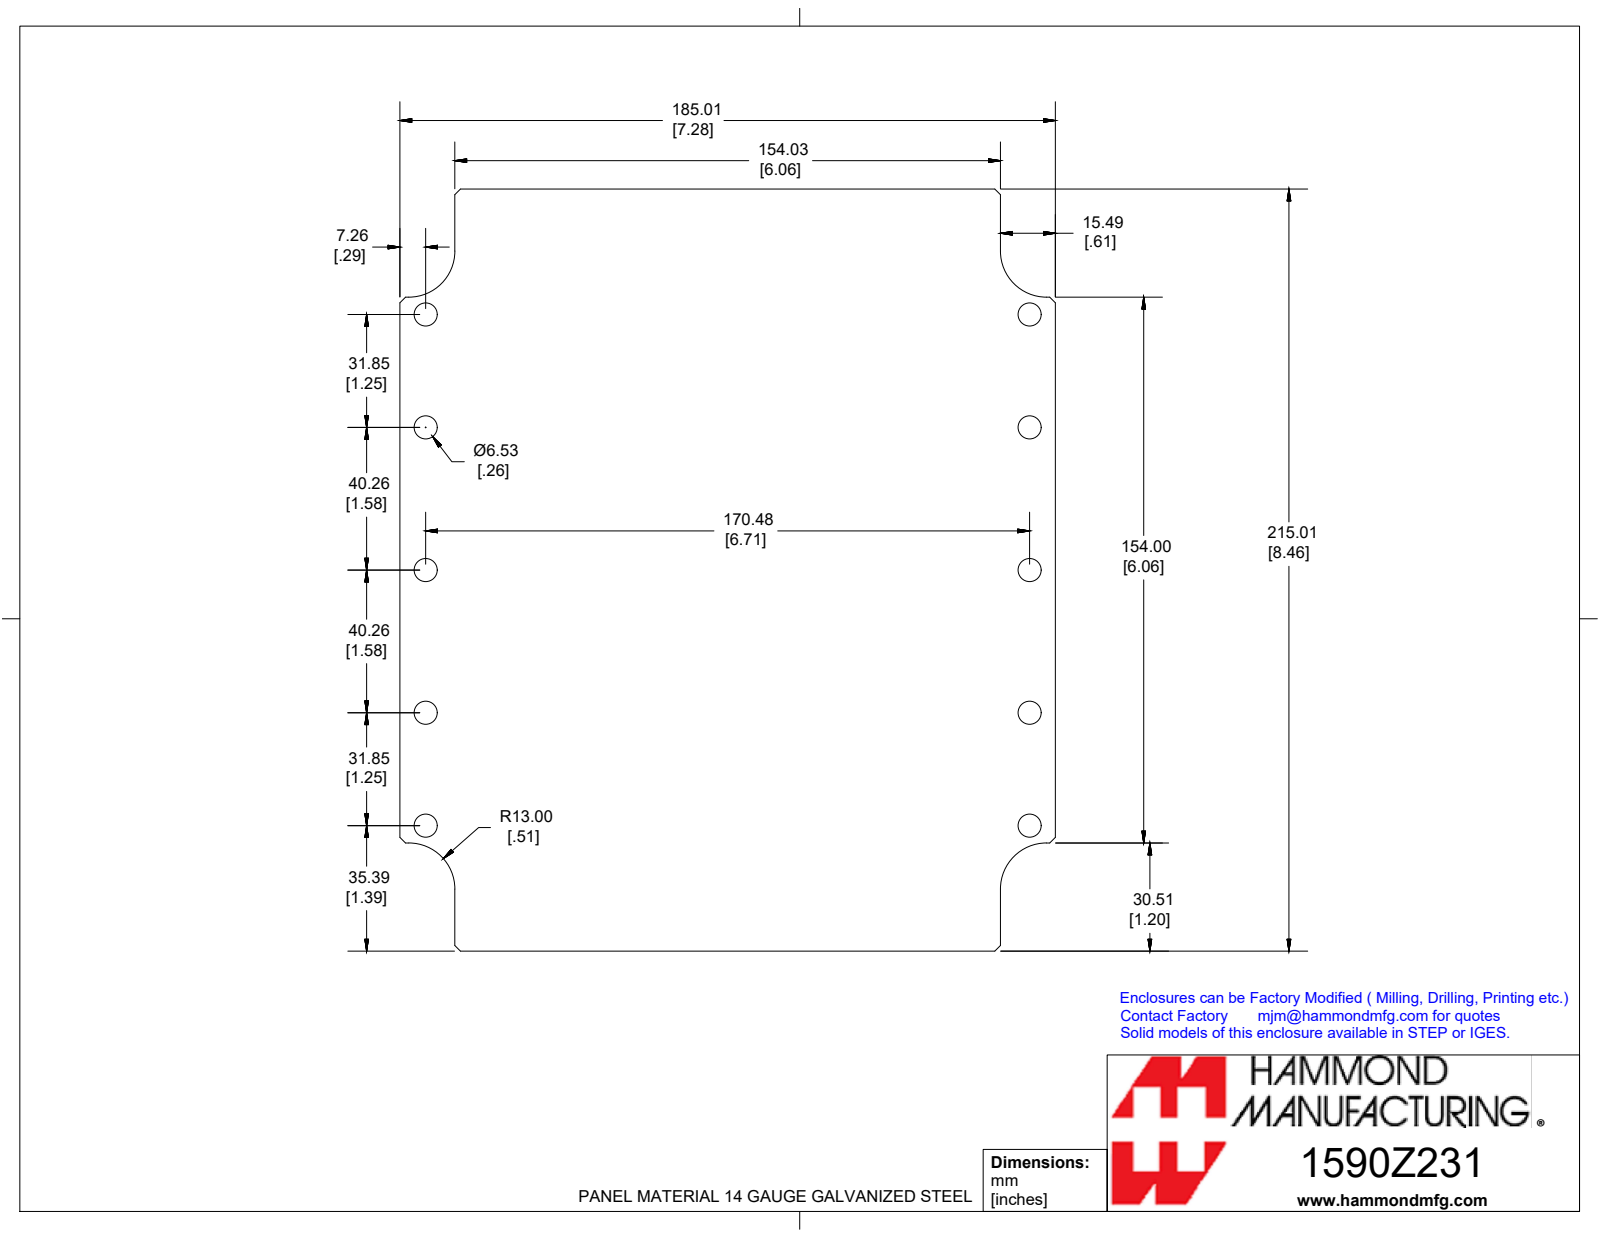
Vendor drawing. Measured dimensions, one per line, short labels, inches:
name: 1590Z231PL
written by: SolidWorks 2019 (CONFIG_CONTROL_DESIGN)
unit: in
bodies: 1 solid, 36 faces (22 planar, 14 cylindrical, 0 other)
size: 8.465 × 7.284 × 0.064
volume: 3.71 in³; area: 119.3 in²
holes: 10× ⌀0.257
rounds: 4× R0.512
face distances: 0.063, 8.465, 7.284, 0.61, 6.674, 6.064, 0.418, 9.766, 9.348, 10.183
hole spacings: 6.712, 1.254, 1.585, 2.839, 4.424, 6.828, 6.896, 7.287
